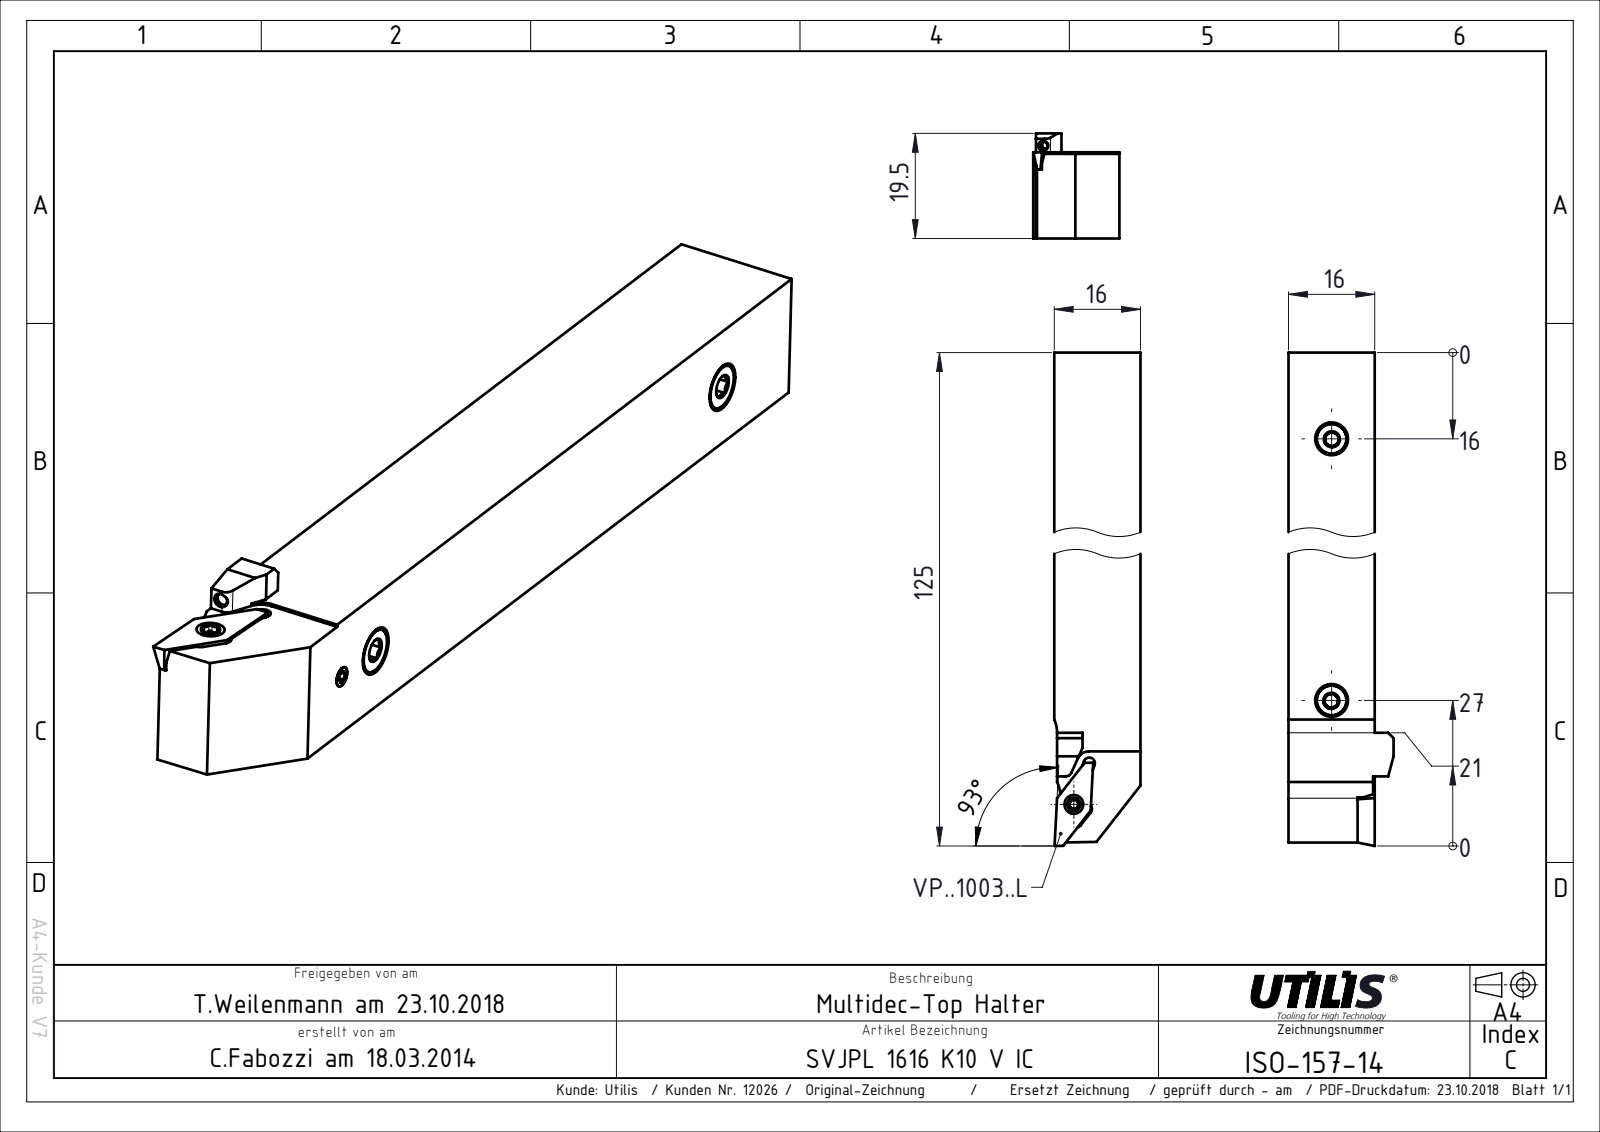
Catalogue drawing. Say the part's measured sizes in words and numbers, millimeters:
The part is named "ISO-157-14". Its 3-D file was written by "SolidWorks 2016 (AUTOMOTIVE_DESIGN)". It is 1 solid with 49 faces: 42 planar, 7 cylindrical and 0 other. Overall it measures 125 by 19.5 by 16.2 millimeters. Its volume is 31 001 cubic millimeters and its surface area 8 461 square millimeters. Partial cylindrical surfaces (rounded edges, fillets, slot ends): 3 of radius 1.05, 2 of radius 6.1, 1 of radius 2.3. The main face-to-face distances are 16, 15.73, 15.7, 19.5, 3.8, 3.5, 12.82, 2.88, 3.18, 6.68.
